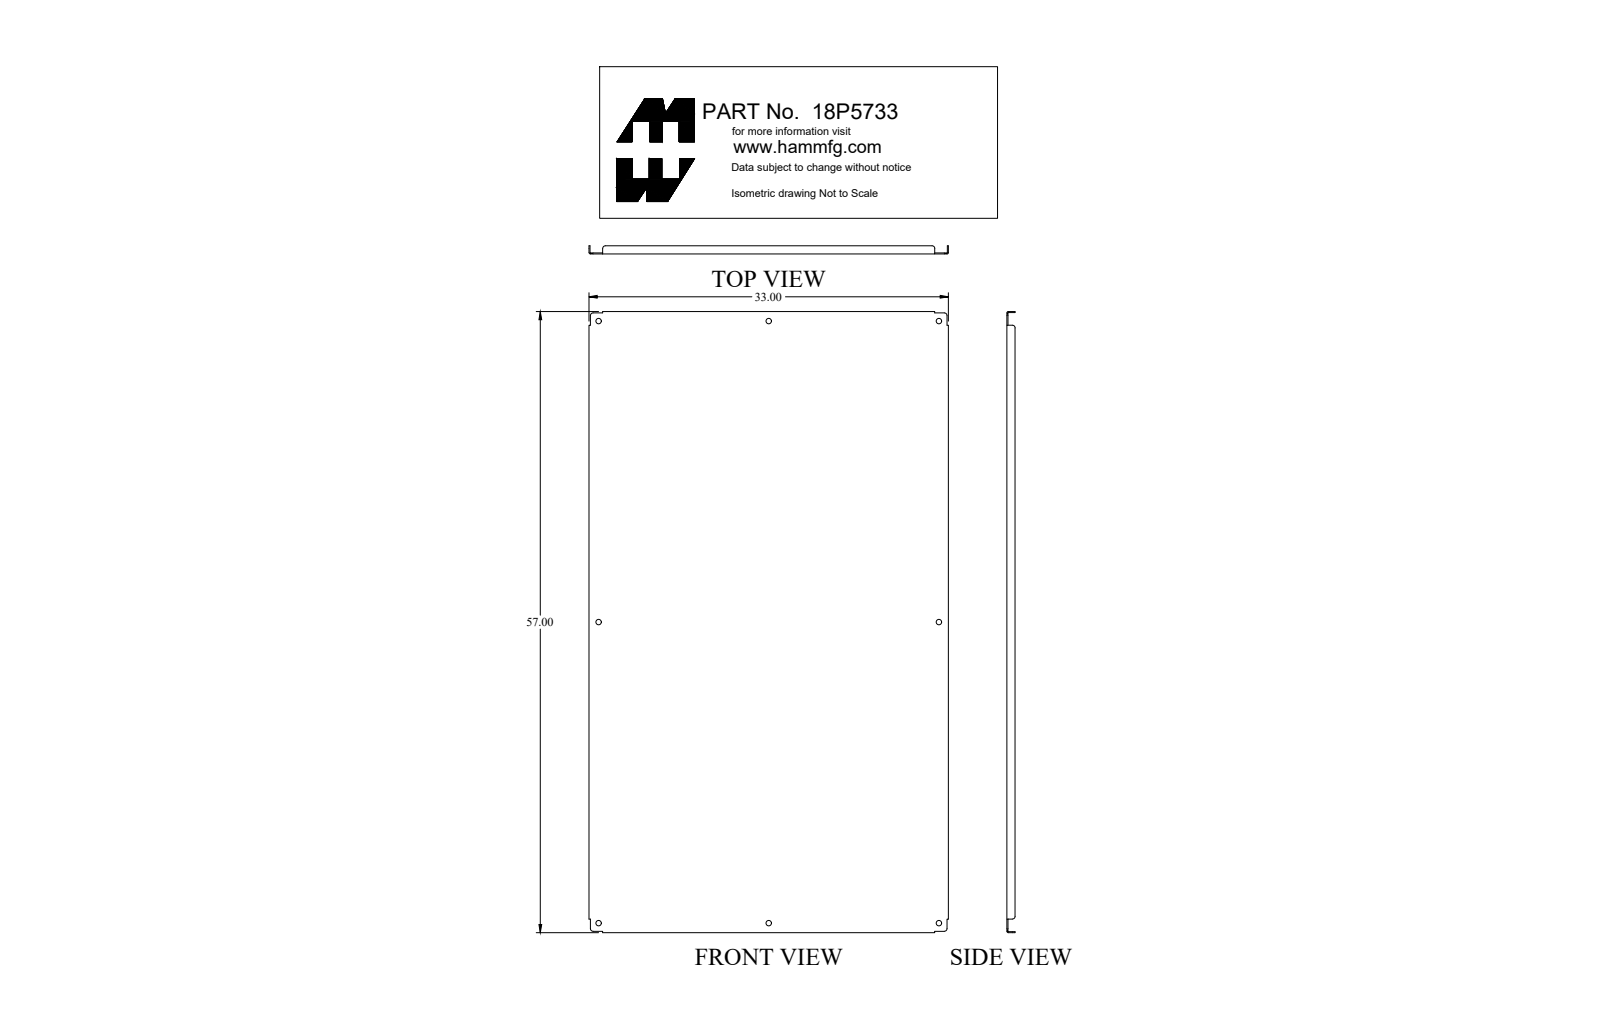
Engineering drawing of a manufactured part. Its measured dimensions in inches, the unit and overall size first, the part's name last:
Units: inches
Overall size (bounding box): 57 × 33 × 0.75
Round holes (diameter × count): ⌀0.5 ×8
Partial cylindrical surfaces — rounded edges, fillets, slot ends (radius × count): R0.25 ×8, R0.03 ×4, R0.125 ×4
Main face-to-face distances: 0.095, 32.905, 56.905, 32.81, 33, 57, 56.81, 0.75, 0.655, 0.125
Hole centre spacings: 15.625, 27.625, 31.738, 41.71, 57.417, 31.25, 55.25, 63.475
Volume: 188.5 in³ · Surface area: 3 986 in²
Bodies: 1 solid, 66 faces (30 planar, 36 cylindrical, 0 other)
Part name (STEP PRODUCT): 18P5733_Default
STEP written by: SolidWorks 2018 (CONFIG_CONTROL_DESIGN)
